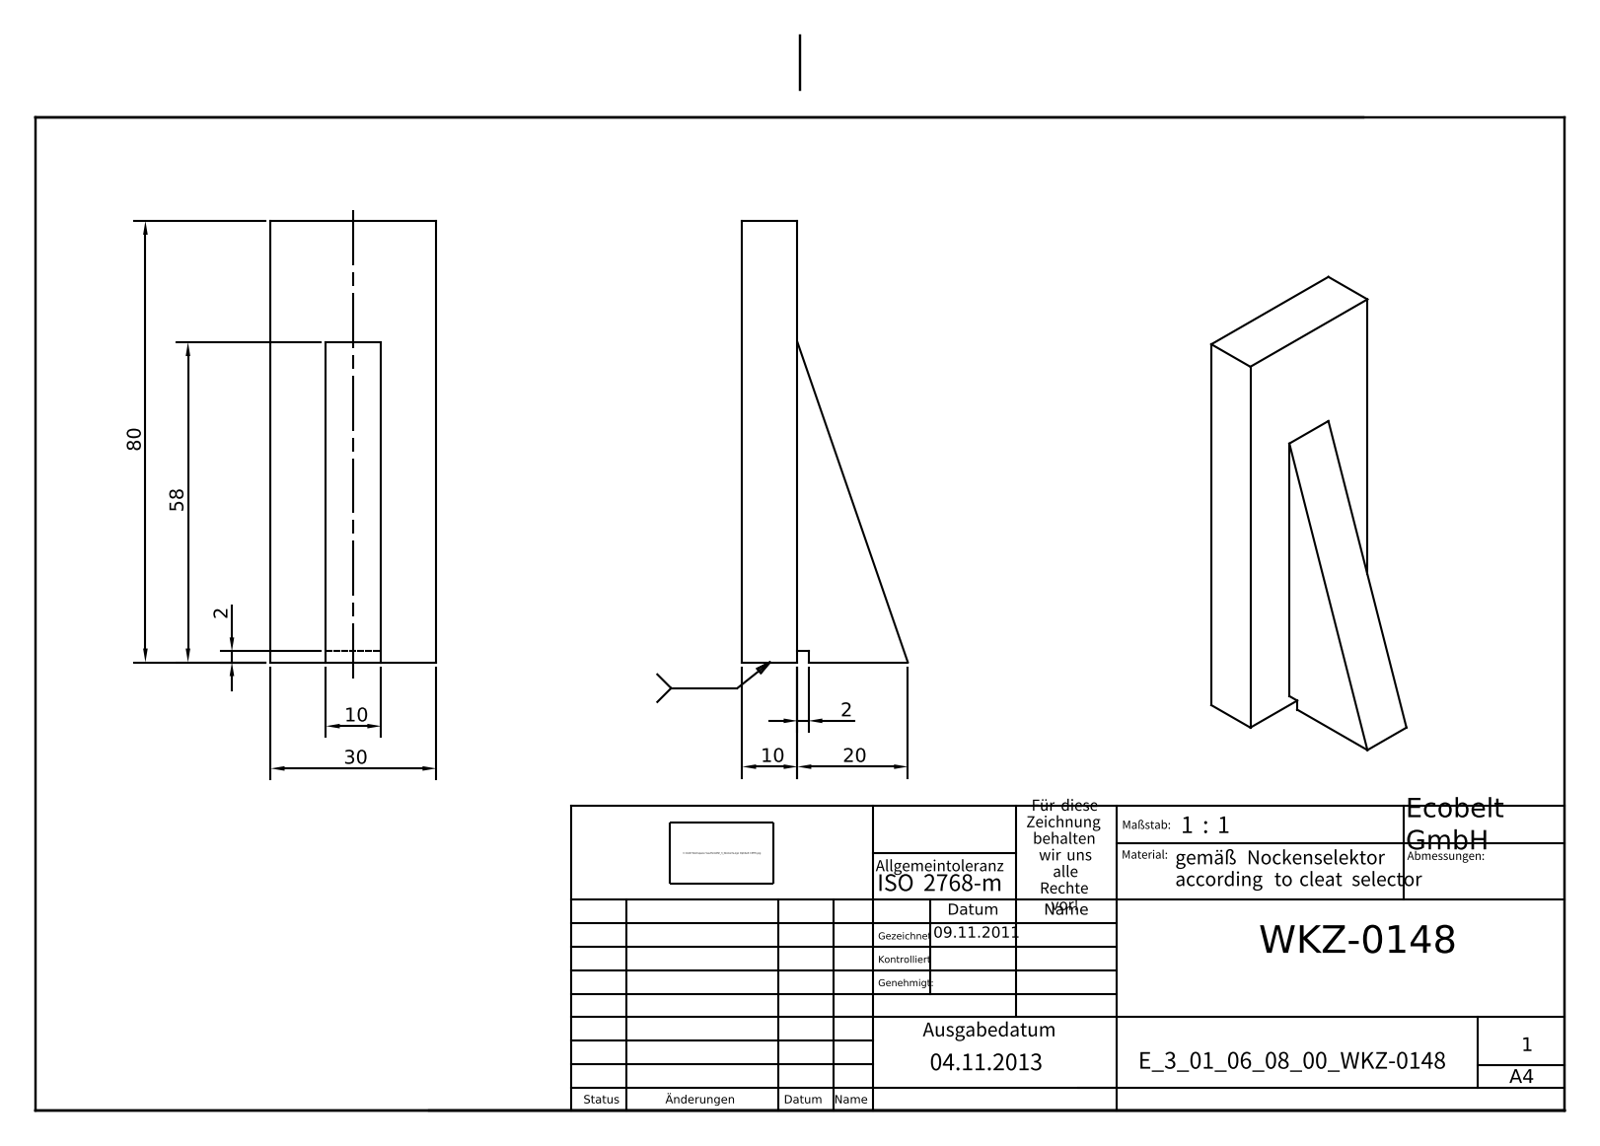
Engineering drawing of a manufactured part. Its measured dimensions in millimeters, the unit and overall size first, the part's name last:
Units: millimetres
Overall size (bounding box): 80 × 30 × 30
Main face-to-face distances: 10, 20, 30, 80, 2, 12, 78
Volume: 29 760 mm³ · Surface area: 8 426 mm²
Bodies: 1 solid, 12 faces (12 planar, 0 cylindrical, 0 other)
Part name (STEP PRODUCT): E_3_01_06_08_00_WKZ-0148
STEP written by: Autodesk Inventor 2025 (AUTOMOTIVE_DESIGN)
